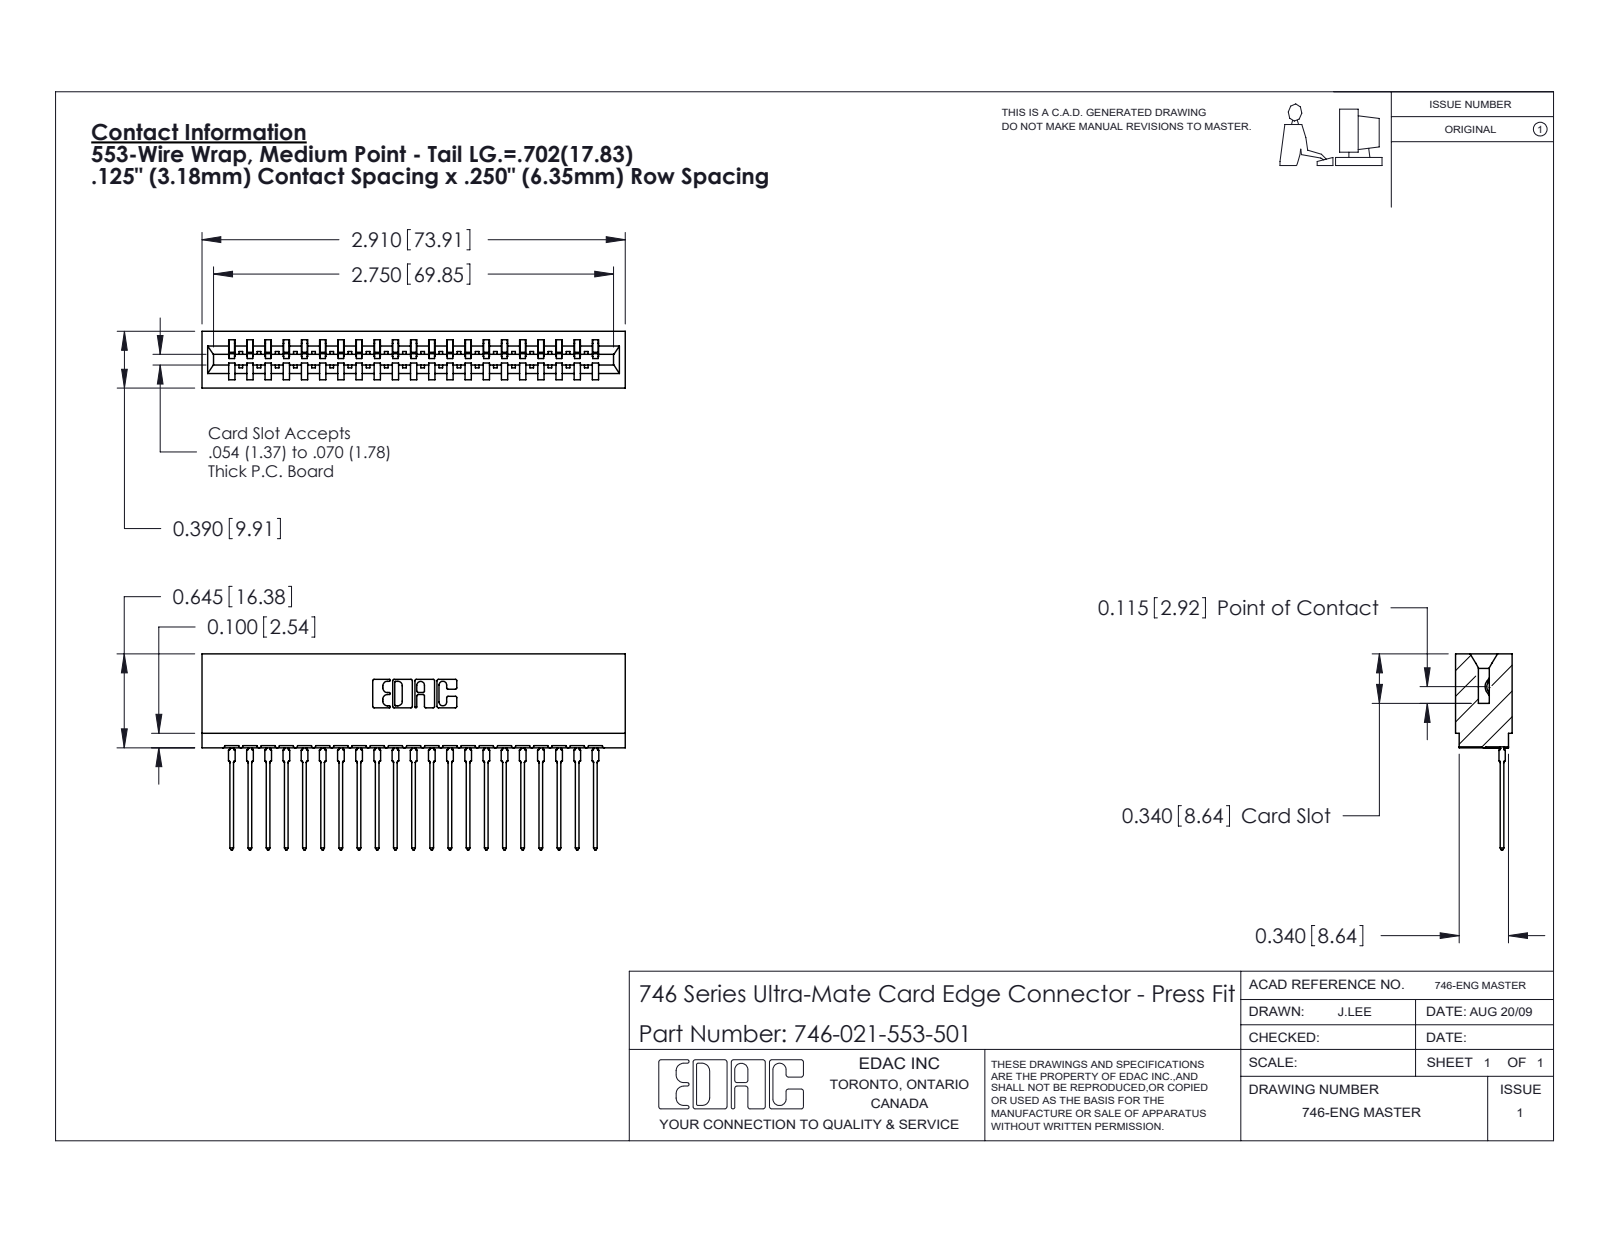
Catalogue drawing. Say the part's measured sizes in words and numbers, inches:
The part is named "746-021-553-501; 746 Part_.340 Slot Depth - 01; 746-292-001_553". Its 3-D file was written by "SolidWorks 2020 (CONFIG_CONTROL_DESIGN)". It is 22 solids with 2365 faces: 1378 planar, 441 cylindrical and 546 other. Overall it measures 2.91 by 1.346 by 0.39 inches. Its volume is 0.519 cubic inches and its surface area 17.9 square inches. Partial cylindrical surfaces (rounded edges, fillets, slot ends): 42 of radius 0.021, 22 of radius 0.01, 22 of radius 0.015, 6 of radius 0.007, 6 of radius 0.031, 4 of radius 0.005, 4 of radius 0.011, 3 of radius 0.026. The main face-to-face distances are 0.25, 0.057, 0.333, 0.39, 0.5, 0.025, 0.307, 0.125, 0.292, 0.125.
